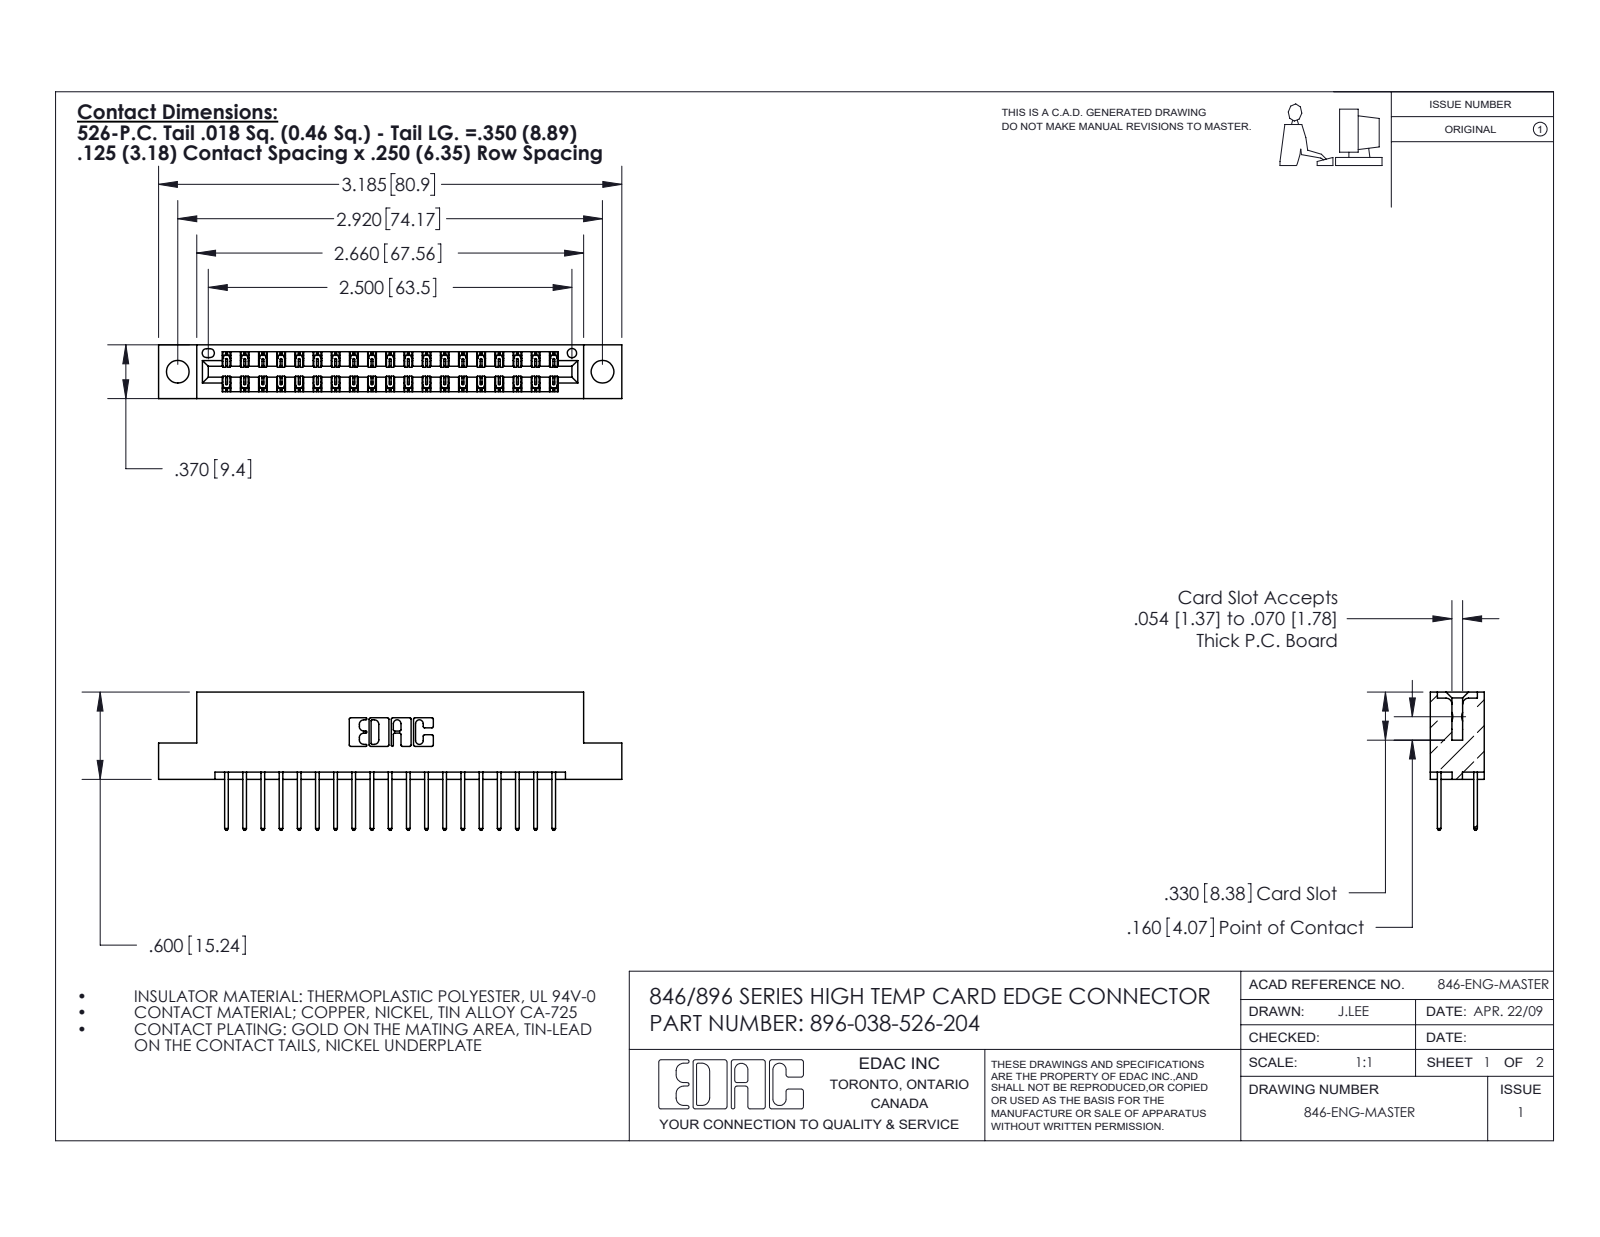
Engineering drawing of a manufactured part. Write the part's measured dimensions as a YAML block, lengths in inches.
part_name: "345-292-001_345-293-126; 346 Part_Flush Mounting Lugs - 0.156 Dia-TH; 396-038-526-204"
step_written_by: "SolidWorks 2016 (CONFIG_CONTROL_DESIGN)"
units: inches
bodies: {solids: 39, faces: 2098, planar: 1406, cylindrical: 692, other: 0}
overall_size: [3.185, 0.95, 0.37]
volume: 0.469
surface_area: 15.96
round_holes:
  - {diameter: 0.156, count: 2}
  - {diameter: 0.064, count: 1}
partial_cylinders:
  - {radius: 0.006, count: 57}
  - {radius: 0.01, count: 38}
  - {radius: 0.01, count: 22}
  - {radius: 0.007, count: 6}
  - {radius: 0.031, count: 6}
  - {radius: 0.026, count: 3}
  - {radius: 0.014, count: 2}
  - {radius: 0.022, count: 2}
face_to_face_distances: [0.048, 0.322, 0.25, 0.37, 0.072, 0.298, 0.025, 0.275, 0.148, 0.222]
hole_center_spacings: [0.246, 2.713, 2.92]
